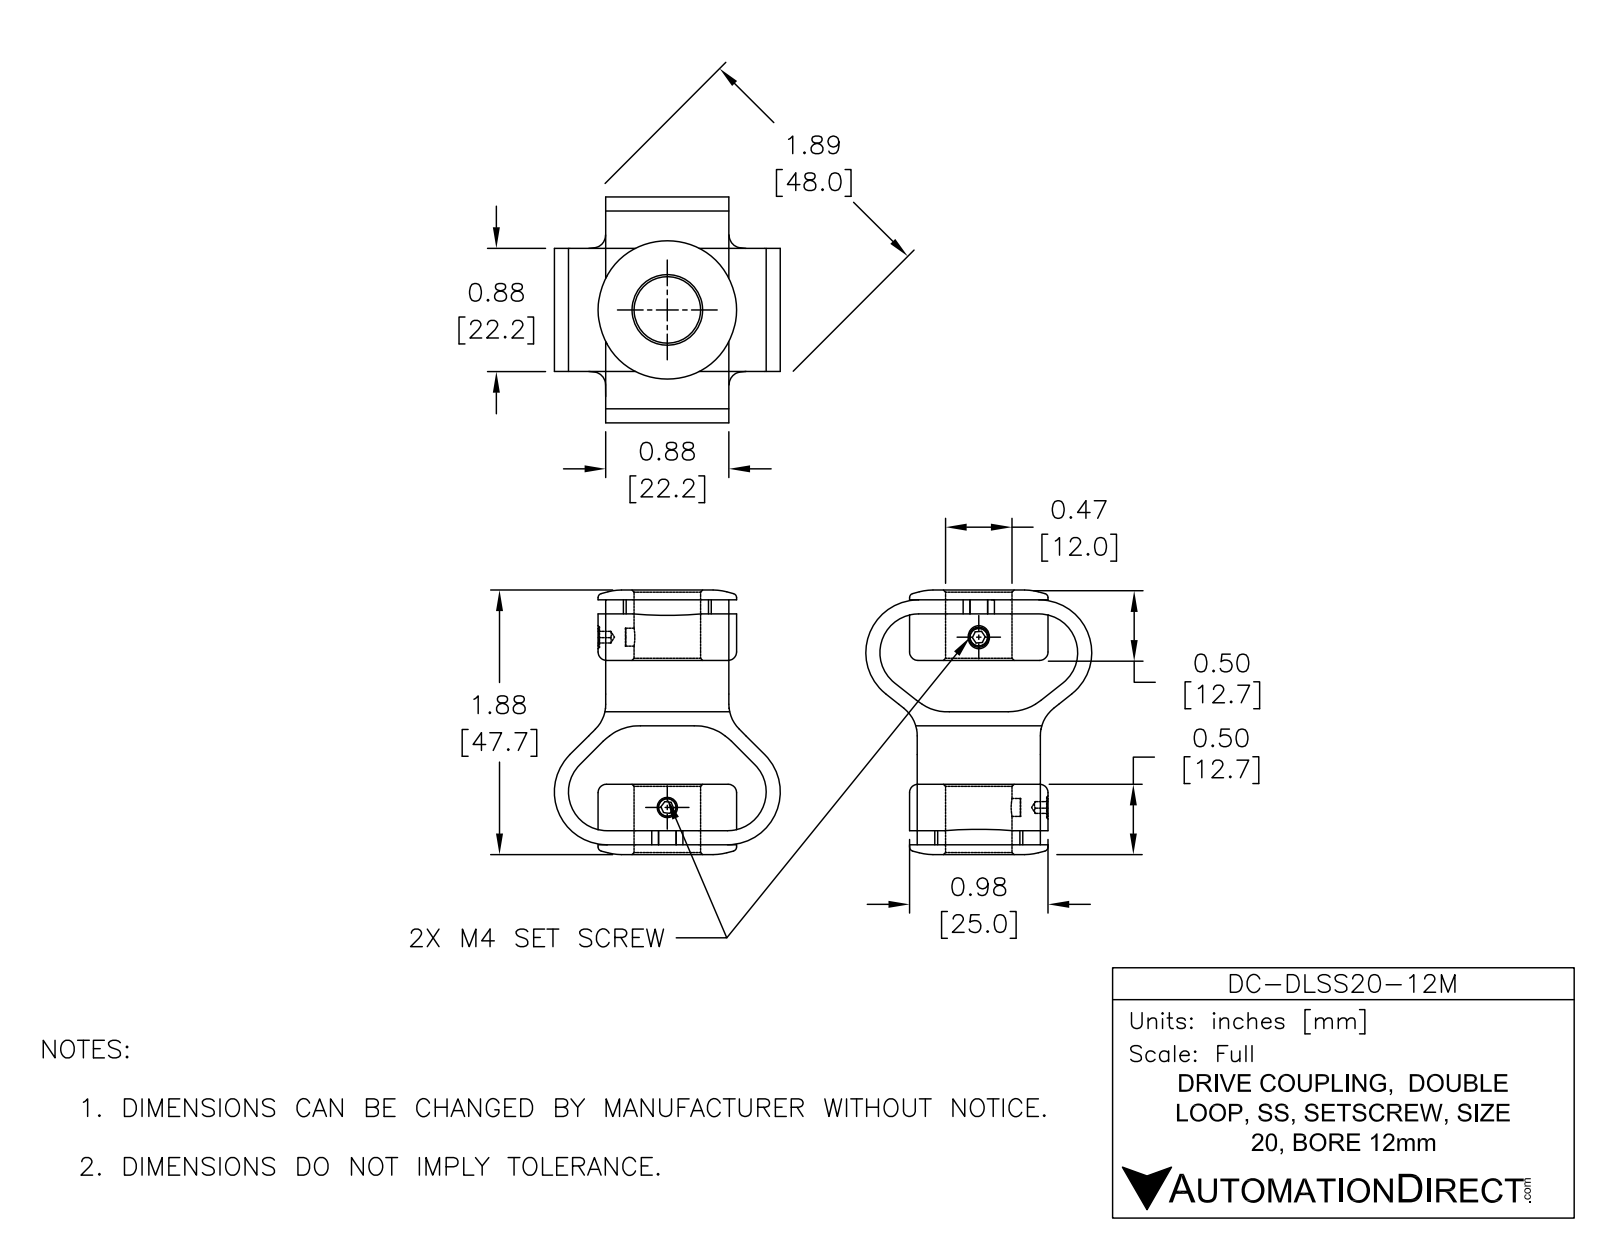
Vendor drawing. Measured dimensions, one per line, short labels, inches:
name: DC-DLSS20-12M
written by: SolidWorks 2015 (AUTOMOTIVE_DESIGN)
unit: in
bodies: 1 solid, 173 faces (90 planar, 47 cylindrical, 36 other)
size: 1.88 × 1.605 × 1.605
volume: 1.013 in³; area: 17.54 in²
holes: 2× ⌀0.128, 1× ⌀0.472
bosses: 1× ⌀0.984
rounds: 7× R0.375, 6× R0.25, 4× R0.275, 3× R0.075, 1× R0.075, 1× R0.313
face distances: 0.1, 0.5, 1.38, 0.07, 1.81, 0.43, 1.31, 0.365, 0.515, 0.88
